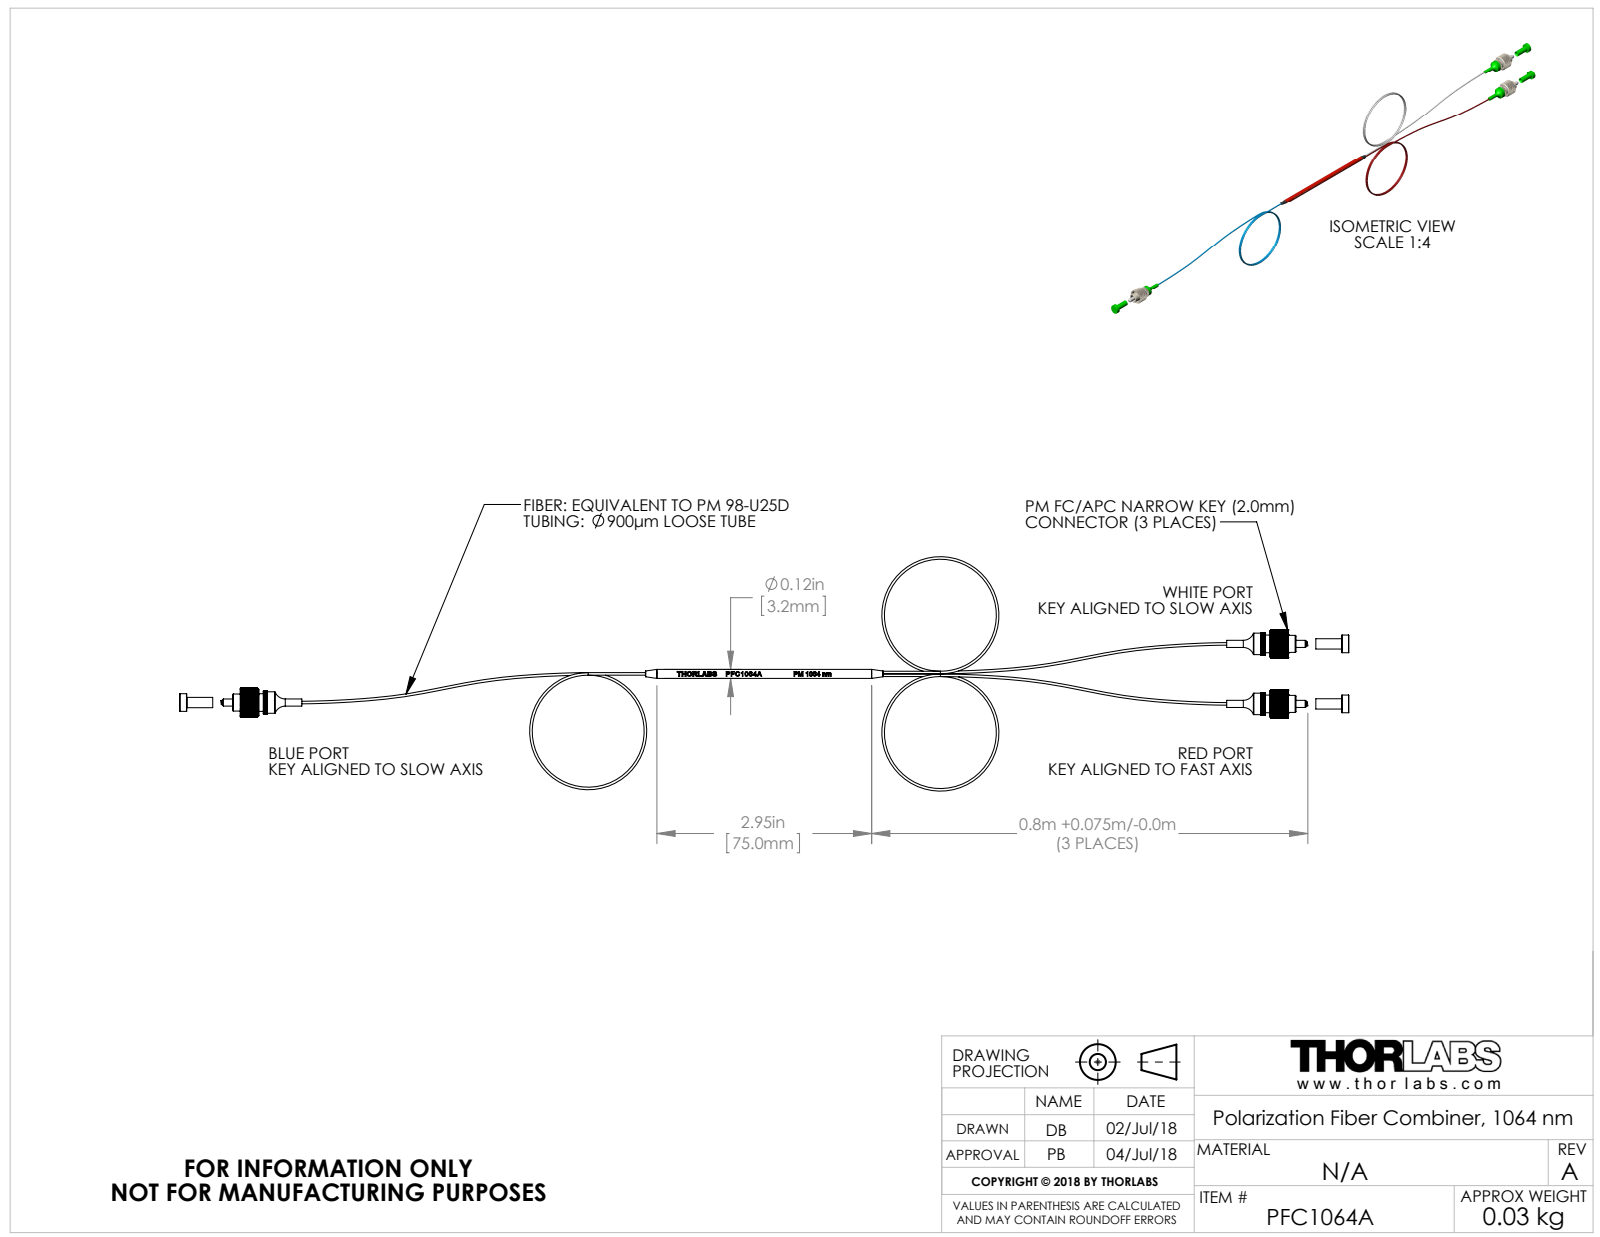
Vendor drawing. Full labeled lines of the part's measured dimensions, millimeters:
Part name (STEP PRODUCT): LA000PLBTTR; DWG1529; DWG1540; DWG1751_45-2mm (+8 more)
STEP written by: SolidWorks 2014 (CONFIG_CONTROL_DESIGN)
Units: millimetres
Bodies: 32 solids, 2628 faces (1277 planar, 895 cylindrical, 456 other)
Overall size (bounding box): 408.3 × 81.85 × 14.2
Volume: 3 280 mm³ · Surface area: 13 594 mm²
Round holes (diameter × count): ⌀0.5 ×6, ⌀0.9 ×3, ⌀0.95 ×3, ⌀1 ×3, ⌀2.5 ×3, ⌀2.8 ×3, ⌀3.36 ×3, ⌀4.38 ×3, ⌀4.4 ×3, ⌀5.08 ×3, ⌀5.55 ×3, ⌀6.1 ×3
Round bosses / shafts (diameter × count): ⌀7.5 ×3, ⌀7.07 ×3, ⌀6.17 ×3, ⌀6.08 ×3, ⌀5.95 ×3, ⌀5.38 ×3, ⌀4.85 ×3, ⌀3.6 ×3
Partial cylindrical surfaces — rounded edges, fillets, slot ends (radius × count): R0.5 ×6, R0.75 ×3, R1.55 ×3, R2.26 ×3, R3.98 ×3, R5 ×3, R0.45 ×2, R1 ×1
Main face-to-face distances: 6.86, 6.85, 2, 1.43, 4.97, 2.97, 349.97, 1.54, 3.43, 27.68
Hole centre spacings: 10.2, 0.47, 0.48, 0.95, 4.03, 9.74, 10.24, 10.66
